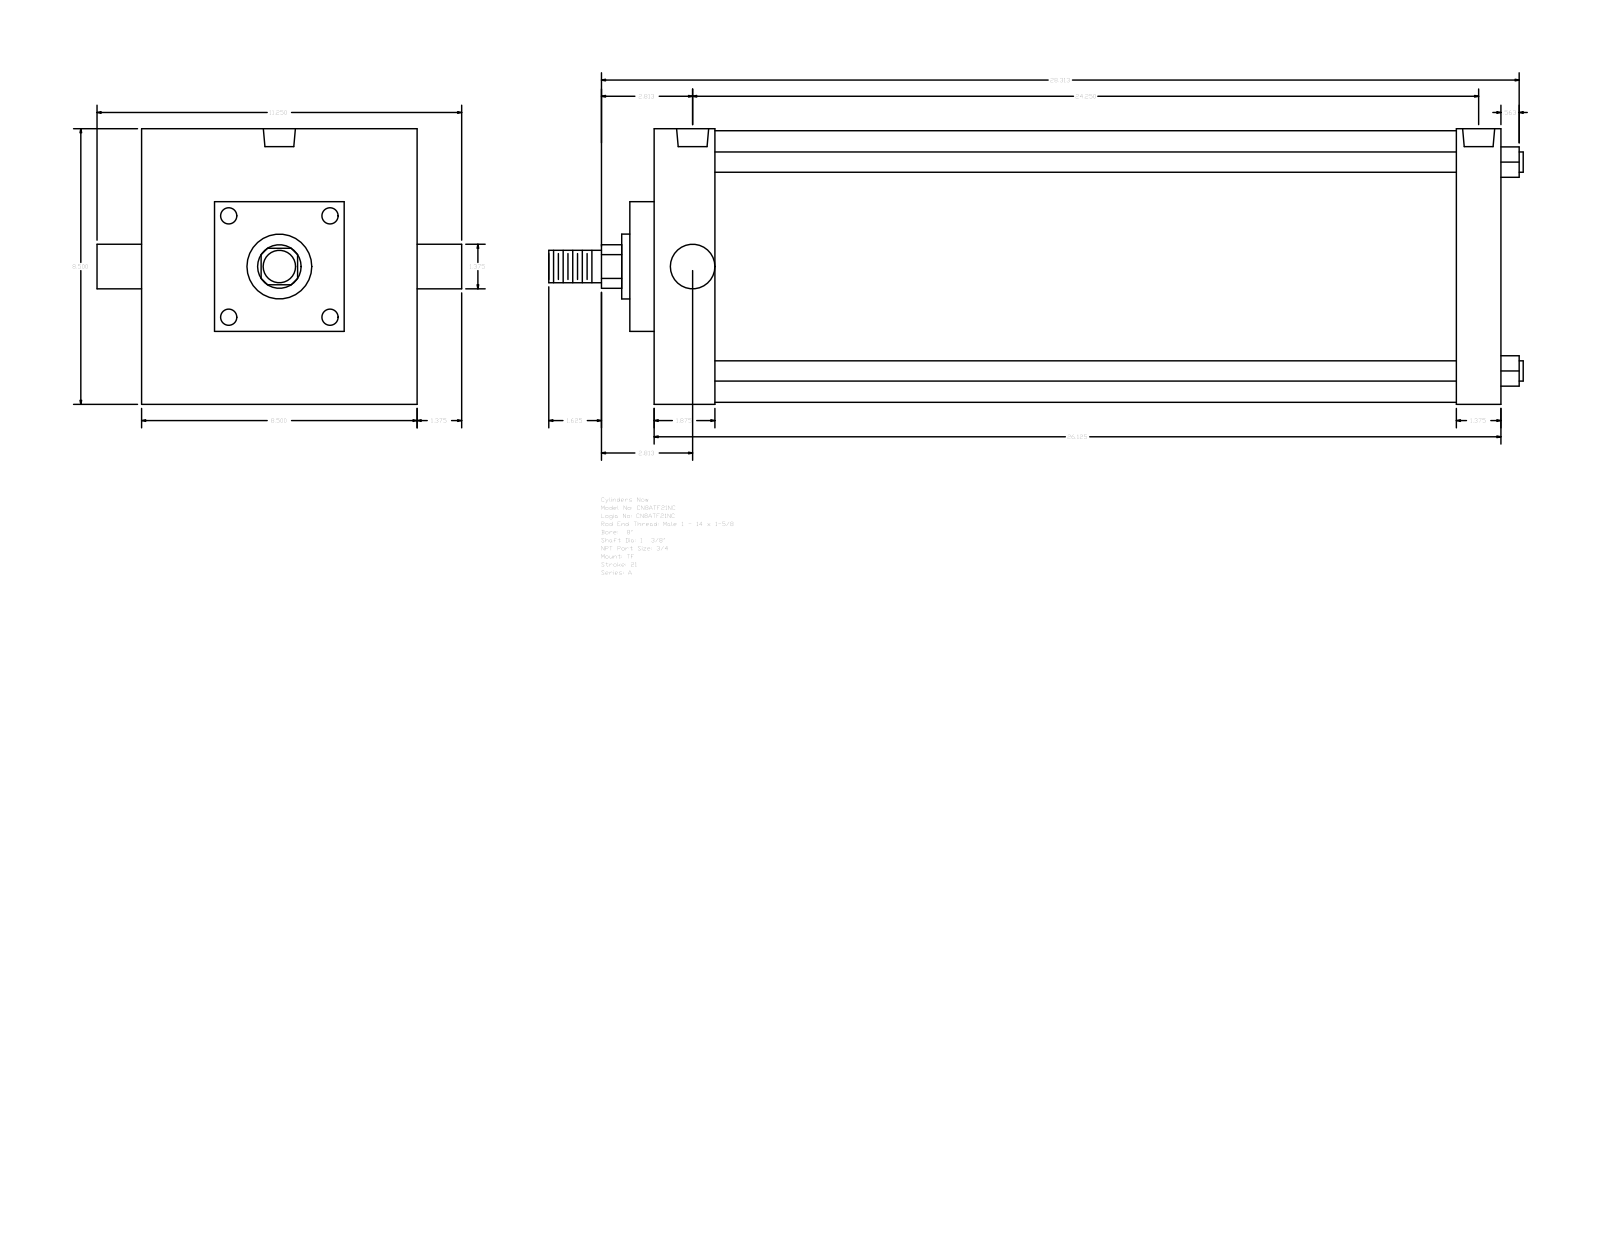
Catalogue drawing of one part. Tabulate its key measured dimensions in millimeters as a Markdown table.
| quantity | value |
| --- | --- |
| part name | A_TF__0800_1.375 |
| STEP written by | GSSL Pune (CONFIG_CONTROL_DESIGN) |
| units | millimeters |
| bodies | 0 solids, 89 faces (65 planar, 24 cylindrical, 0 other) |
| overall size | 763.59 × 285.75 × 215.9 |
| round holes (diameter × count) | 15.08 × 3, 25.12 × 2 |
| round bosses / shafts (diameter × count) | 15.88 × 4, 34.92 × 2, 212.72 × 1, 50.8 × 1, 25.4 × 1 |
| partial cylindrical surfaces (radius × count) | 17.06 × 1 |
| main face-to-face distances | 663.58, 215.9, 34.93, 47.63, 615.95, 628.65, 581.02, 19.04, 66.67, 647.69 |
| hole center spacings | 6.35, 609.6, 603.25, 615.95 |
